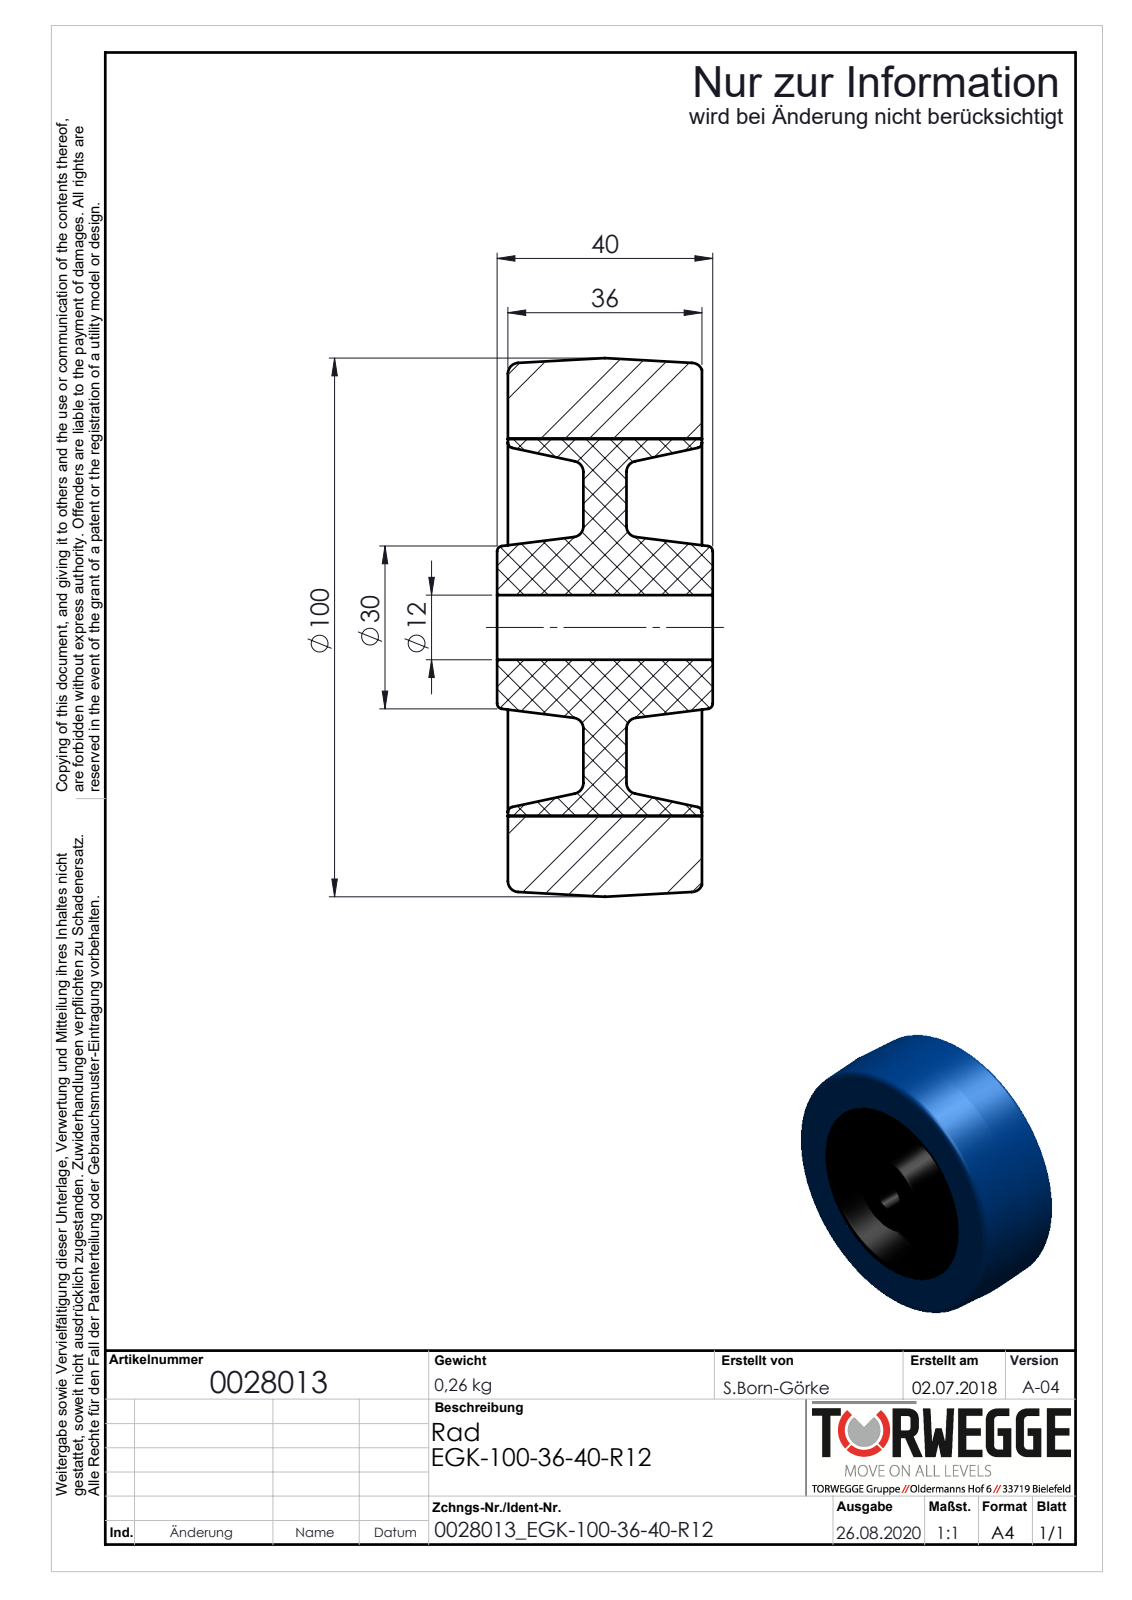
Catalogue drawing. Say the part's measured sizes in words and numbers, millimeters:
The part is named "0028013". Its 3-D file was written by "SolidWorks 2018 (AUTOMOTIVE_DESIGN)". It is 2 solids with 46 faces: 8 planar, 6 cylindrical and 32 other. Overall it measures 100 by 100 by 40 millimeters. Its volume is 208 076 cubic millimeters and its surface area 49 871 square millimeters. Round holes: 1 of diameter 12, 1 of diameter 70. The main face-to-face distances are 36, 14, 22, 8, 2, 16, 24, 38, 40.
